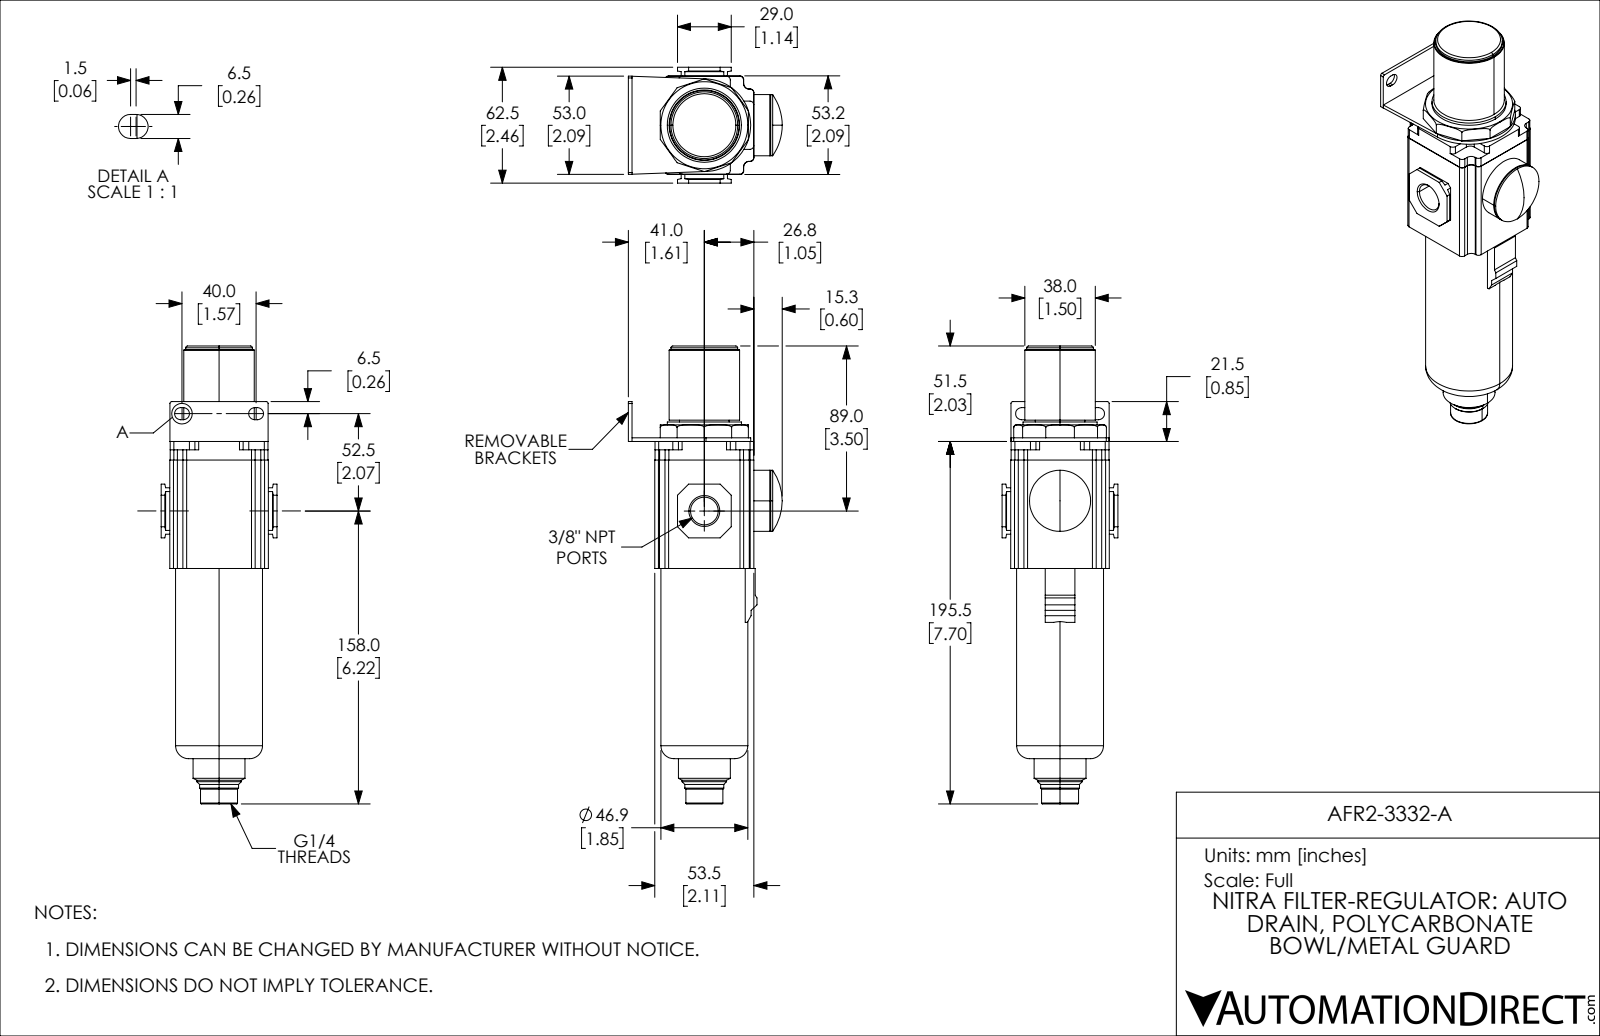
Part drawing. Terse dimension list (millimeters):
name: AFR2-3332-A
written by: SolidWorks 2019 (CONFIG_CONTROL_DESIGN)
unit: mm
bodies: 1 solid, 221 faces (124 planar, 71 cylindrical, 26 other)
size: 247 × 83.03 × 62.5
volume: 449 570 mm³; area: 52 239 mm²
holes: 1× ⌀11.45, 1× ⌀14.95
bosses: 1× ⌀46.9, 1× ⌀40, 1× ⌀38, 1× ⌀36, 1× ⌀33, 1× ⌀28, 1× ⌀26.78, 1× ⌀24
rounds: 24× R2, 12× R3, 4× R3.25, 2× R1, 1× R25
face distances: 2, 53.2, 53.5, 14.25, 4.65, 57.85, 12.25, 67.75, 51.5, 49.5
